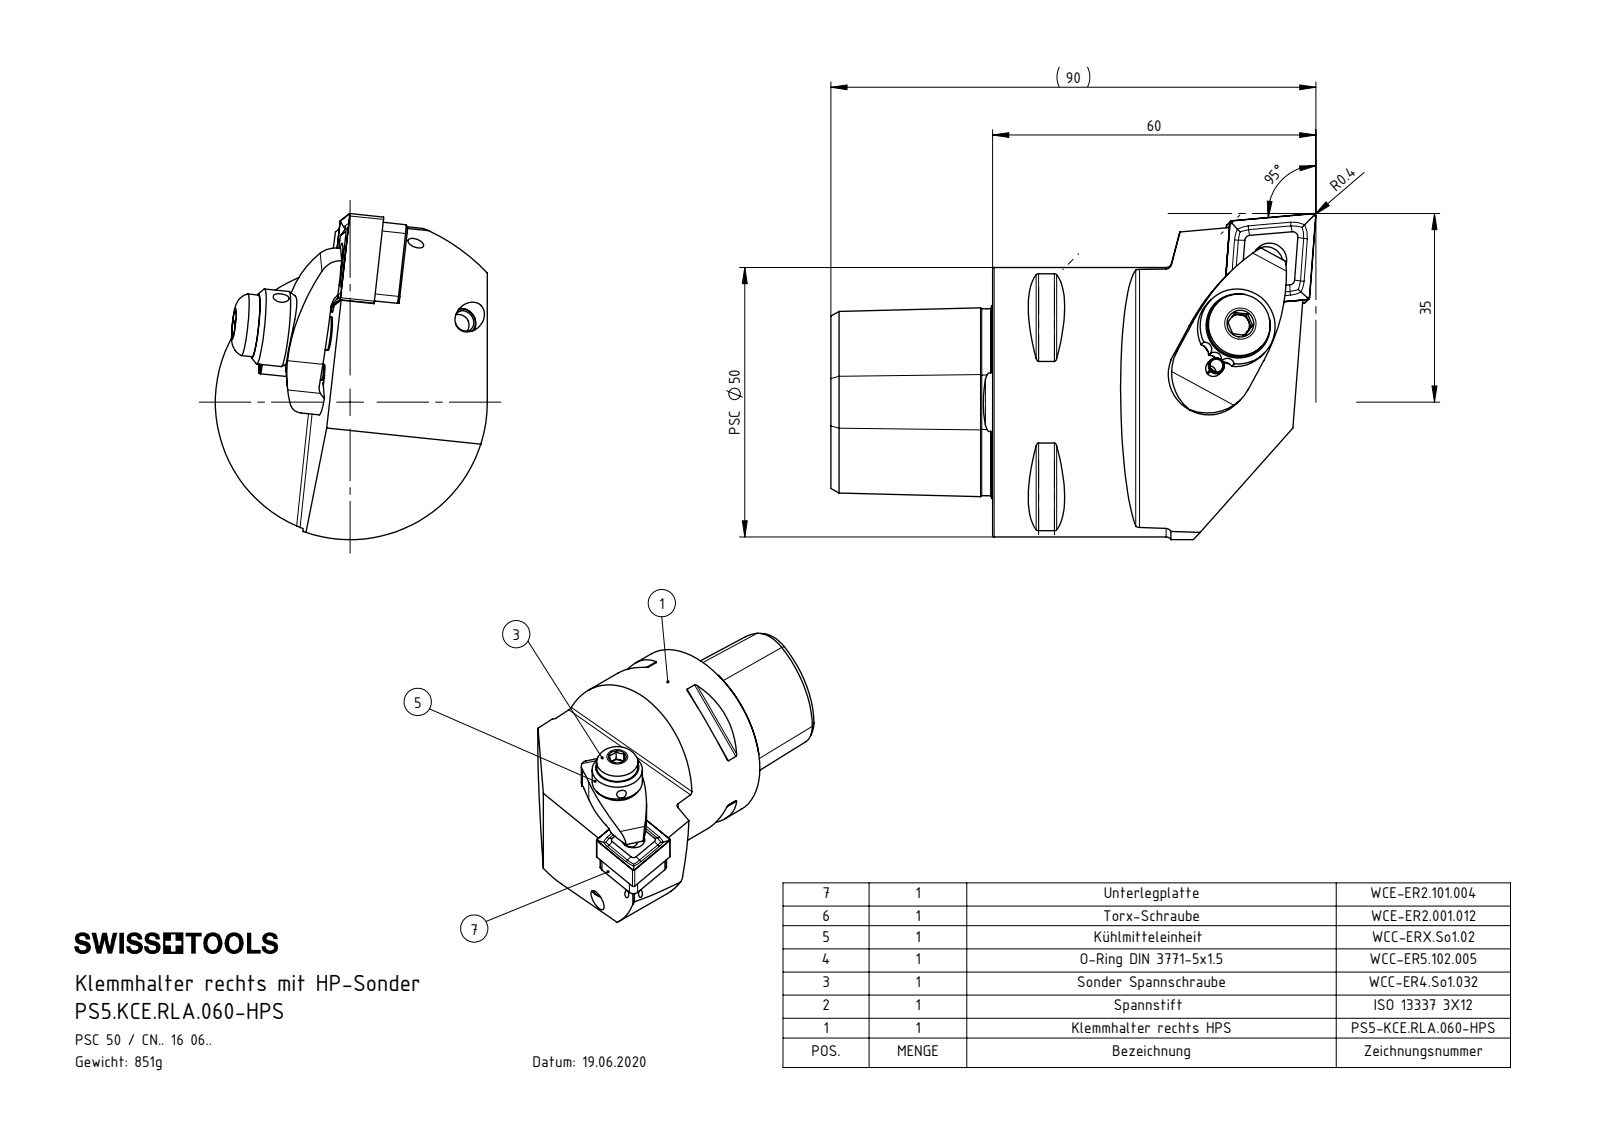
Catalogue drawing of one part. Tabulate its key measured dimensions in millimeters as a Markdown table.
| quantity | value |
| --- | --- |
| part name | WCE-ER2.101.004_A; KVT_MB_600_050; WCC-ER4.So1.032_A; WCC-ER5.So1.012_B (+7 more) |
| STEP written by | SolidWorks 2017 (AUTOMOTIVE_DESIGN) |
| units | millimeters |
| bodies | 11 solids, 326 faces (108 planar, 97 cylindrical, 121 other) |
| overall size | 90 × 60.5 × 50.5 |
| volume | 107 607 mm³ |
| surface area | 25 620 mm² |
| round holes (diameter × count) | 1.5 × 3, 2.7 × 3, 4.2 × 3, 4 × 2, 5 × 2, 2 × 1, 2.4 × 1, 3 × 1, 6.1 × 1, 6.2 × 1, 6.35 × 1, 7 × 1 |
| round bosses / shafts (diameter × count) | 5 × 2, 50 × 1, 14 × 1, 11.5 × 1, 6.8 × 1, 6 × 1, 4 × 1, 3 × 1 |
| partial cylindrical surfaces (radius × count) | 0.5 × 8, 1.5 × 7, 0.45 × 6, 0.4 × 4, 0.79 × 4, 7 × 3, 0.79 × 2, 2 × 2 |
| main face-to-face distances | 6.05, 30, 4.76, 10.81, 14.68, 1.3, 1.2, 12.11, 7.35, 19.18 |
| hole center spacings | 6.07, 8.2, 10.59, 10.79, 13.79, 15.41, 15.6, 23.61 |
